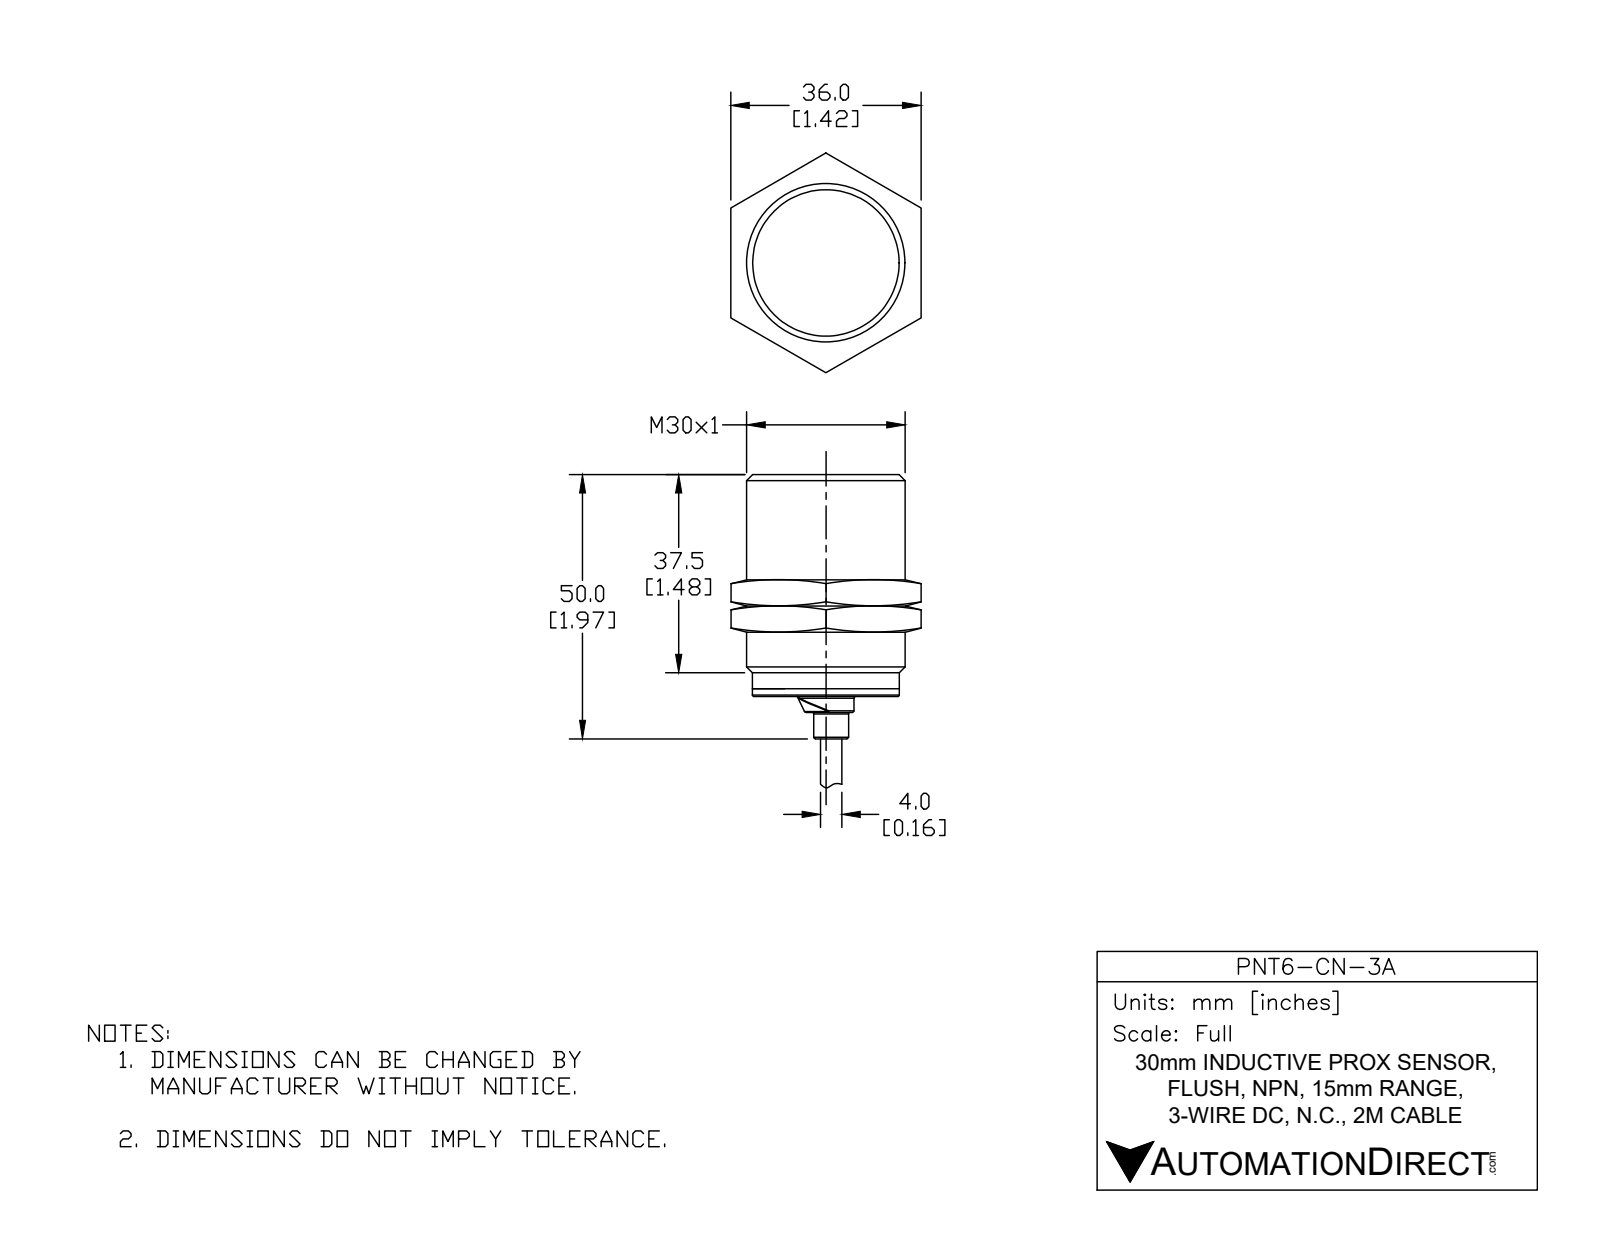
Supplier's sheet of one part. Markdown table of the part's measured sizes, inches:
| quantity | value |
| --- | --- |
| part name | PNT6-CN-3A |
| STEP written by | SolidWorks 2017 (AUTOMOTIVE_DESIGN) |
| units | inches |
| bodies | 1 solid, 77 faces (15 planar, 30 cylindrical, 32 other) |
| overall size | 3.969 × 1.181 × 1.181 |
| volume | 1.84 in³ |
| surface area | 9.715 in² |
| round holes (diameter × count) | 0.162 × 1 |
| round bosses / shafts (diameter × count) | 0.049 × 6, 1.181 × 1, 1.095 × 1, 1.094 × 1, 0.417 × 1, 0.26 × 1, 0.157 × 1 |
| partial cylindrical surfaces (radius × count) | 0.077 × 1 |
| main face-to-face distances | 1.654, 1.772, 0.118, 1.969, 0.315, 0.197, 3.969, 2.315, 2.197, 2 |
